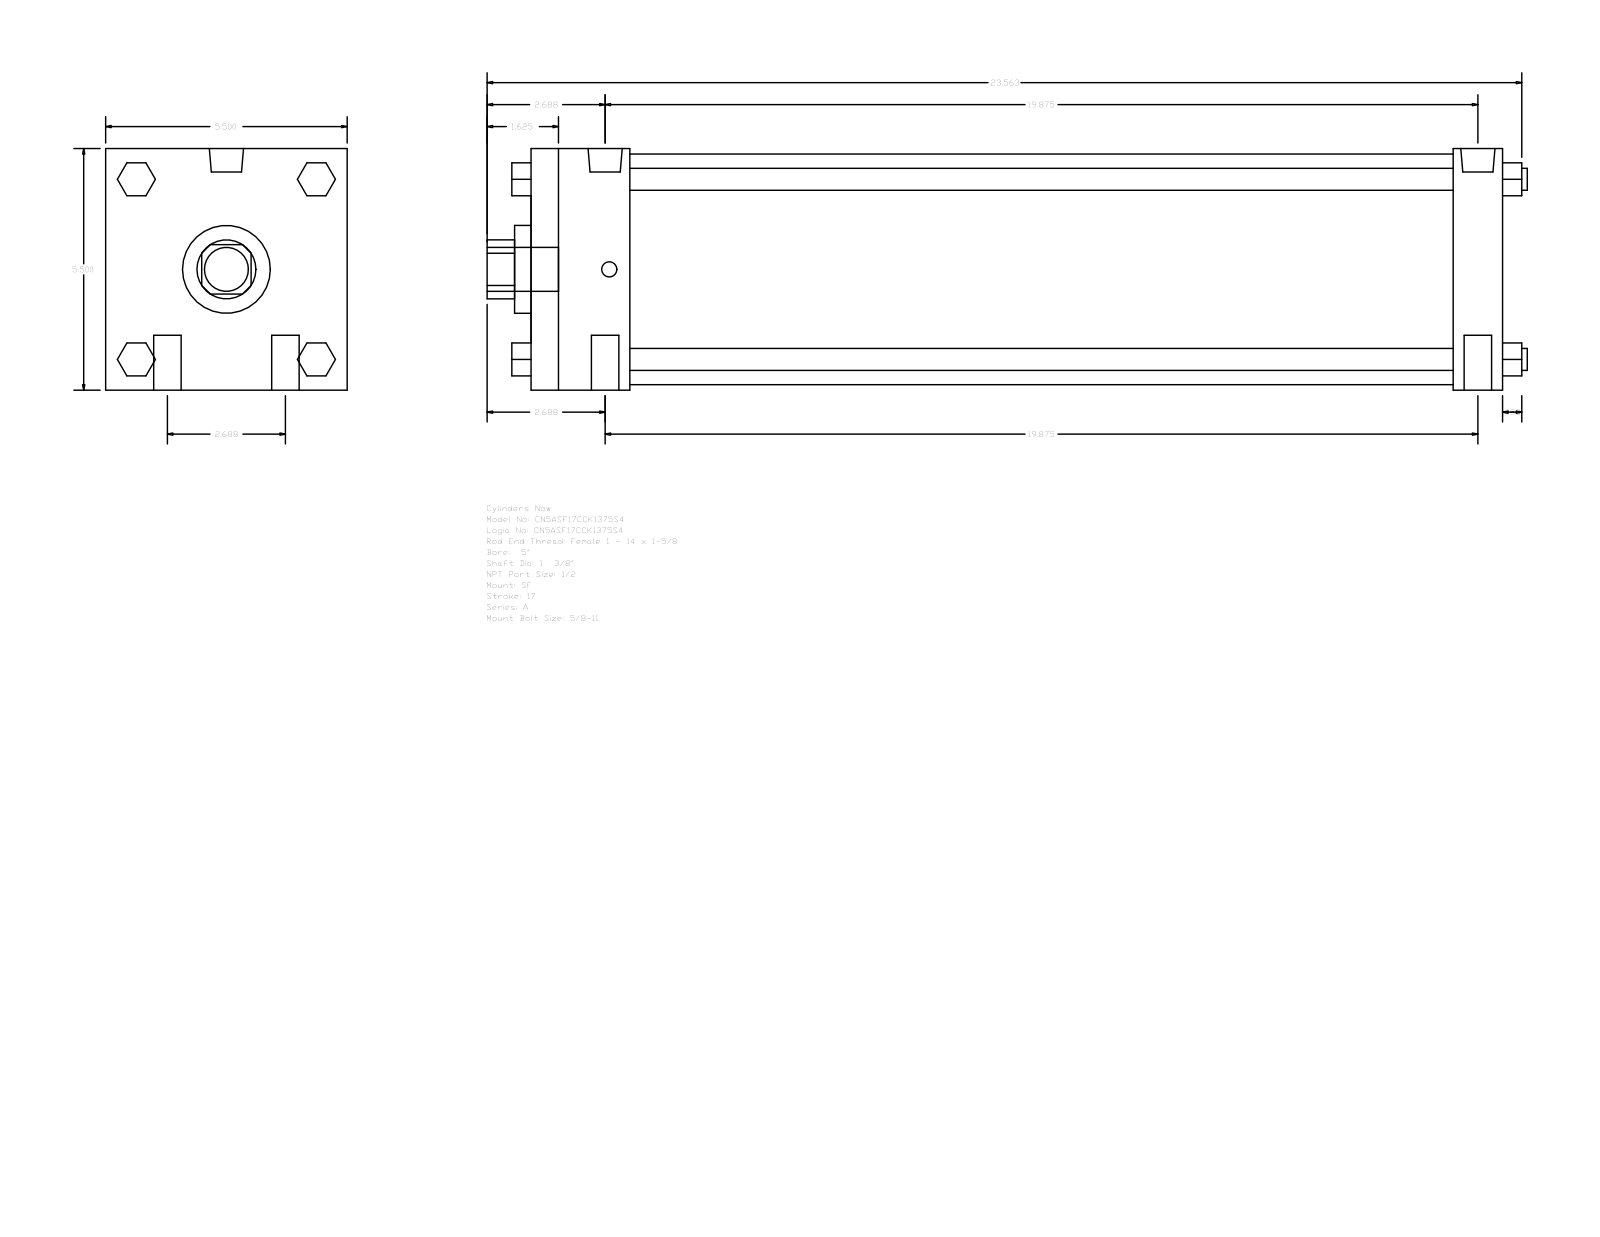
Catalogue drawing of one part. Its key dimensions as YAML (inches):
part_name: "A_SF__0500_1.375"
step_written_by: "GSSL Pune (CONFIG_CONTROL_DESIGN)"
units: inches
bodies: {solids: 0, faces: 124, planar: 94, cylindrical: 30, other: 0}
overall_size: [23.687, 5.5, 5.5]
round_holes:
  - {diameter: 1.375, count: 1}
  - {diameter: 2, count: 1}
  - {diameter: 5.25, count: 1}
round_bosses_or_shafts:
  - {diameter: 0.625, count: 4}
  - {diameter: 0.5, count: 4}
  - {diameter: 0.778, count: 2}
  - {diameter: 0.344, count: 2}
  - {diameter: 1, count: 1}
partial_cylinders:
  - {radius: 0.672, count: 1}
face_to_face_distances: [5.5, 22.125, 1.125, 2.25, 21, 18.75, 19.875, 0.75, 2.05, 3.55]
